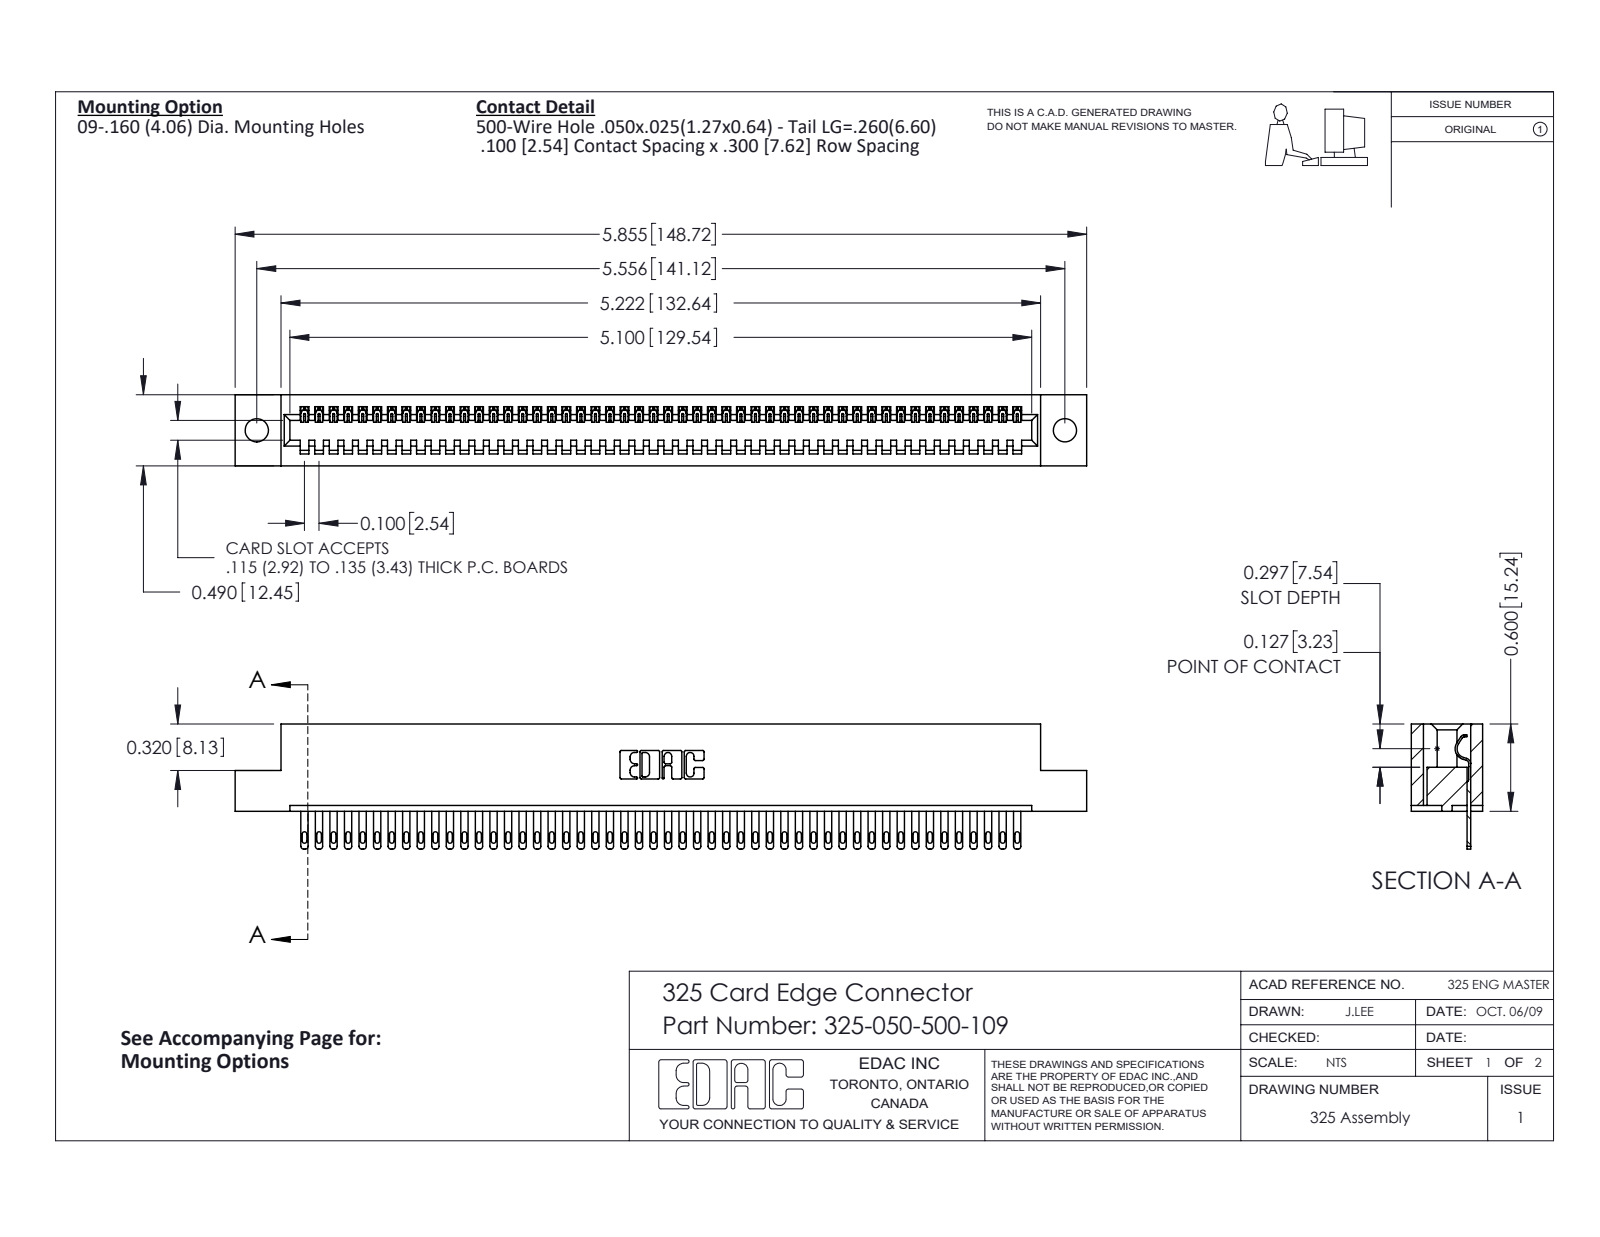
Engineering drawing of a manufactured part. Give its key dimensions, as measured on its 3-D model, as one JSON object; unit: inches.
{"part_name": "325-292-001_325-293-100; 325-050-500-109; 325 Part_.160 TH", "step_written_by": "SolidWorks 2016 (CONFIG_CONTROL_DESIGN)", "units": "inches", "bodies": {"solids": 51, "faces": 2814, "planar": 1870, "cylindrical": 944, "other": 0}, "overall_size": [5.855, 0.86, 0.49], "volume_in3": 1.144, "surface_area_in2": 31.97, "round_holes": [[0.16, 2]], "partial_cylinders_radius": [[0.006, 100], [0.016, 100], [0.02, 100], [0.01, 22], [0.007, 6], [0.031, 6], [0.026, 3], [0.014, 1]], "face_to_face_distances": [0.083, 0.407, 0.49, 0.3, 0.107, 0.383, 0.025, 0.325, 0.56, 0.263], "hole_center_spacings": [5.556]}
